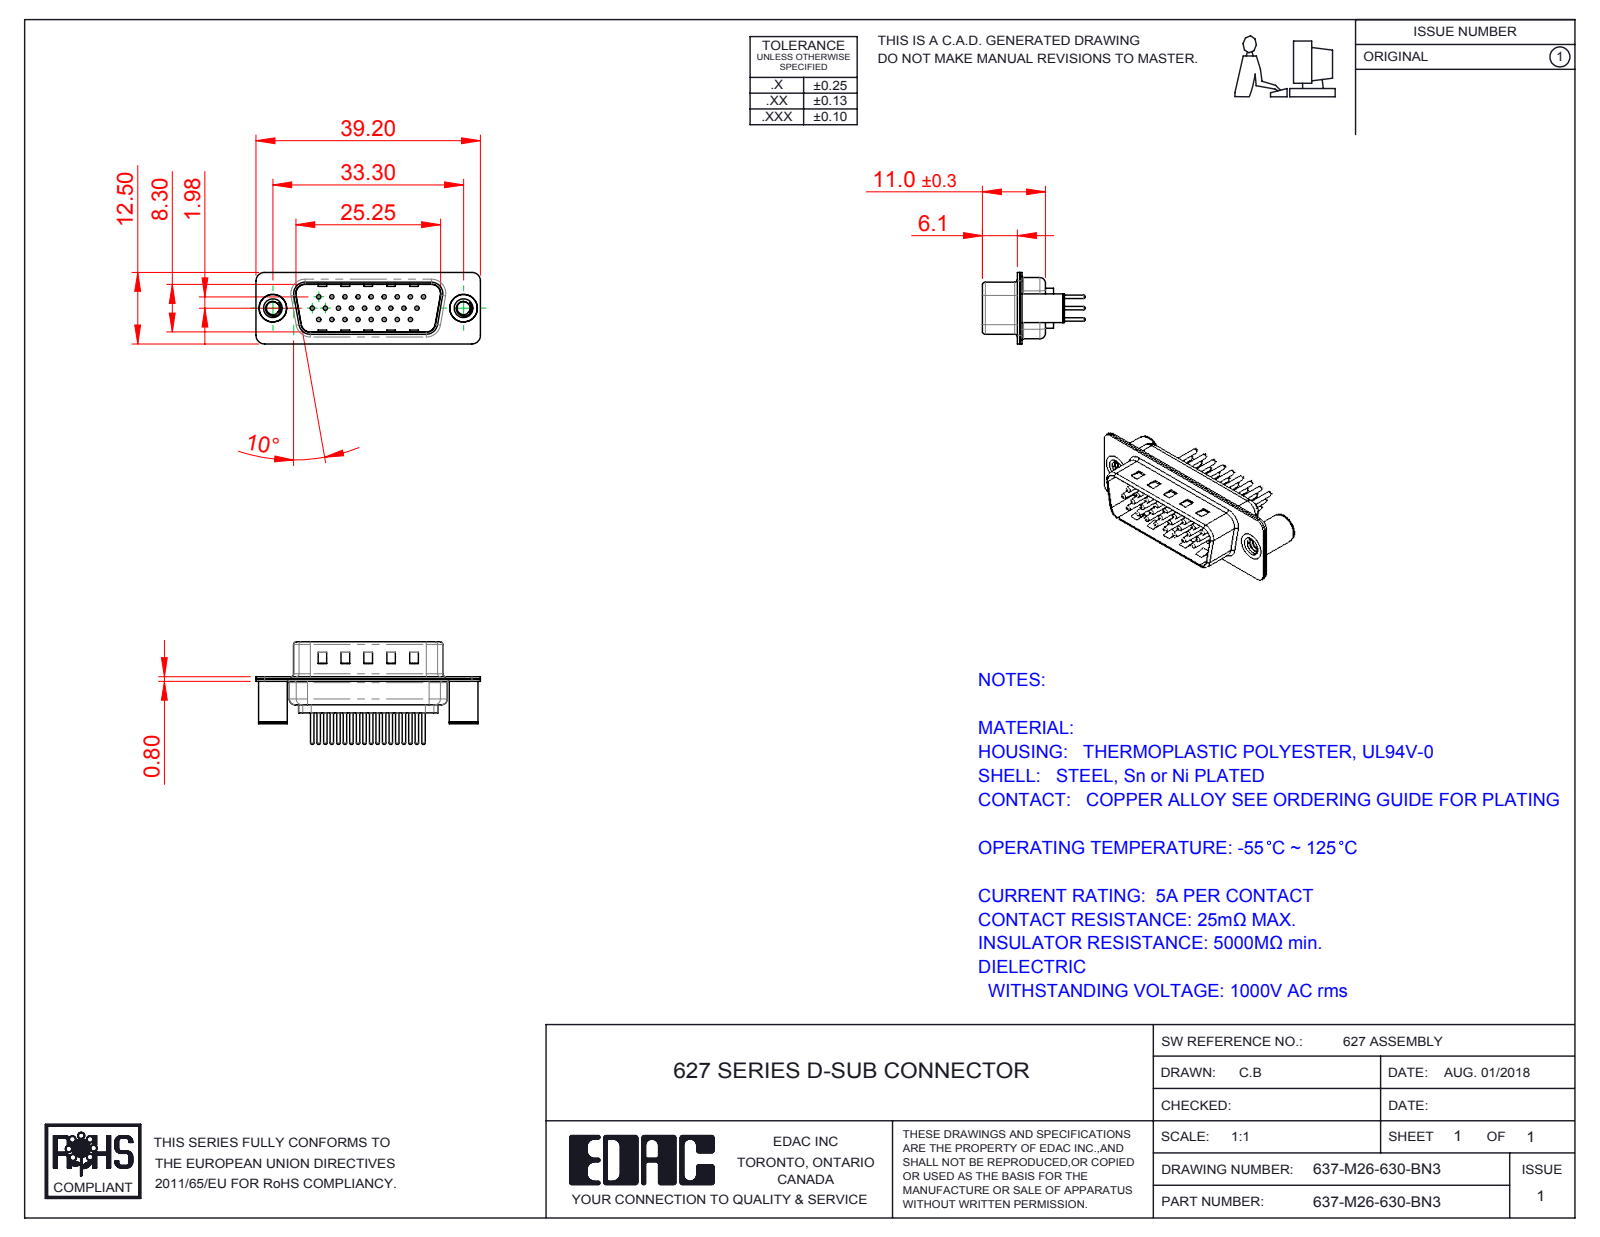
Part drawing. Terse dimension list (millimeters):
name: 637-M26-630-BN3; 637M Housing_26 Contacts; 637M Shell Front_26 Contacts; 637M Contact Row 1_30 (+4 more)
written by: SolidWorks 2016 (CONFIG_CONTROL_DESIGN)
unit: mm
bodies: 31 solids, 1336 faces (321 planar, 521 cylindrical, 494 other)
size: 39.2 × 17.9 × 12.5
volume: 2 032 mm³; area: 6 009 mm²
holes: 26× ⌀0.75, 26× ⌀1.6, 26× ⌀2, 2× ⌀2.26, 2× ⌀3.26, 2× ⌀4, 2× ⌀4.8
bosses: 26× ⌀1.5, 26× ⌀0.6, 2× ⌀5, 2× ⌀4.9
rounds: 16× R1.5, 12× R2, 8× R0.5, 8× R1.6, 4× R0.25, 4× R0.6, 4× R0.65, 4× R0.9
face distances: 0.4, 0.8, 9.5, 9.1, 8.7, 9.9, 6.3, 0.75, 5.5, 0.35
hole spacings: 3.96, 2.28, 4.57, 6.05, 2.29, 8.24, 6.86, 10.48
